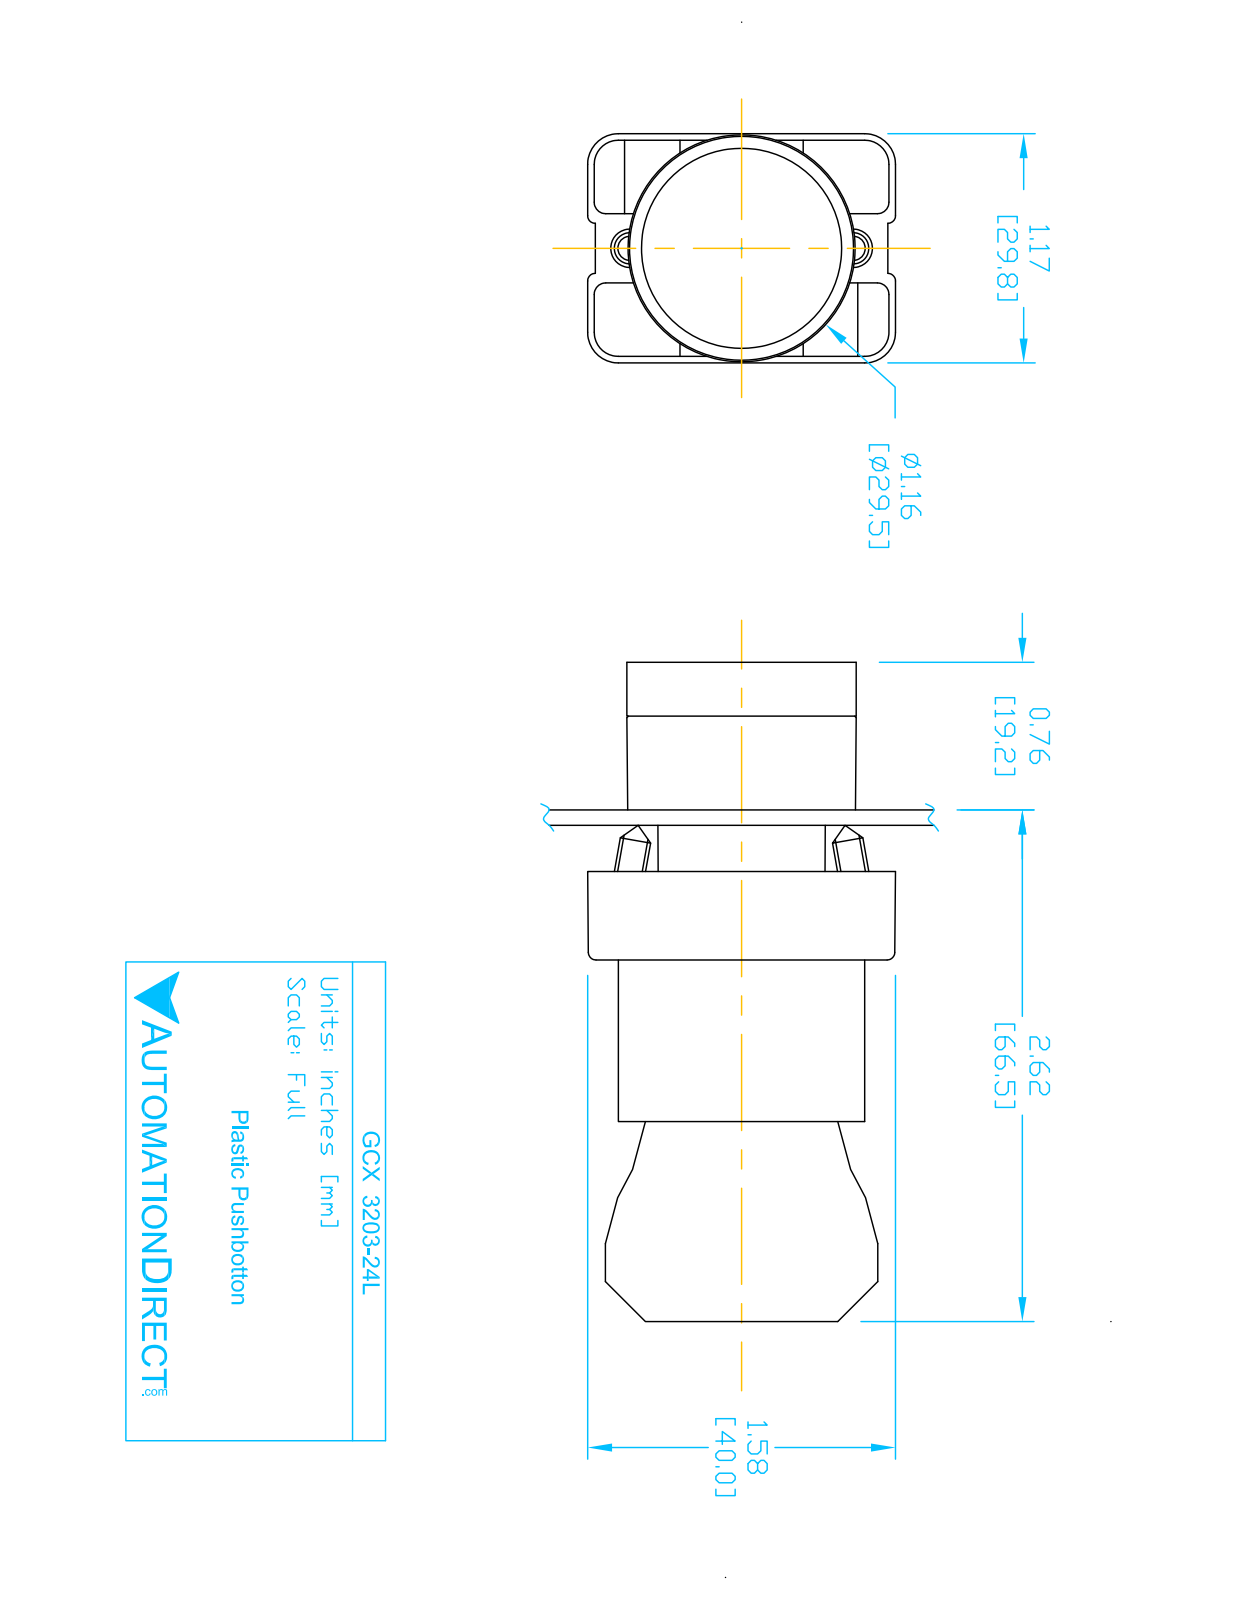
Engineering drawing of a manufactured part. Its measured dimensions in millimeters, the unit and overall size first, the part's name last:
Units: millimetres
Overall size (bounding box): 84.3 × 40.2 × 29.9
Round holes (diameter × count): ⌀2 ×2, ⌀3.1 ×2, ⌀3.3 ×2, ⌀2.2 ×1, ⌀5 ×1, ⌀11.9 ×1, ⌀22.3 ×1, ⌀22.6 ×1, ⌀26 ×1
Round bosses / shafts (diameter × count): ⌀4 ×4, ⌀29.8 ×1, ⌀25.5 ×1, ⌀24 ×1, ⌀21.7 ×1, ⌀19.8 ×1, ⌀12.8 ×1
Partial cylindrical surfaces — rounded edges, fillets, slot ends (radius × count): R1.5 ×24, R1 ×12, R3.1 ×12, R4 ×12, R1 ×8, R3.3 ×2, R0.5 ×1, R1.6 ×1
Main face-to-face distances: 21, 14.7, 51.3, 30.3, 29.7, 7, 58.3, 37.3, 0.8, 0.8
Hole centre spacings: 6, 13.8, 12, 12.4
Volume: 45 790 mm³ · Surface area: 25 010 mm²
Bodies: 8 solids, 431 faces (252 planar, 148 cylindrical, 31 other)
Part name (STEP PRODUCT): GCX3203L OPERATOR; ECX3029-2; GCX3203-24L; ecx1040 (+1 more)
STEP written by: SolidWorks 2016 (AUTOMOTIVE_DESIGN)
